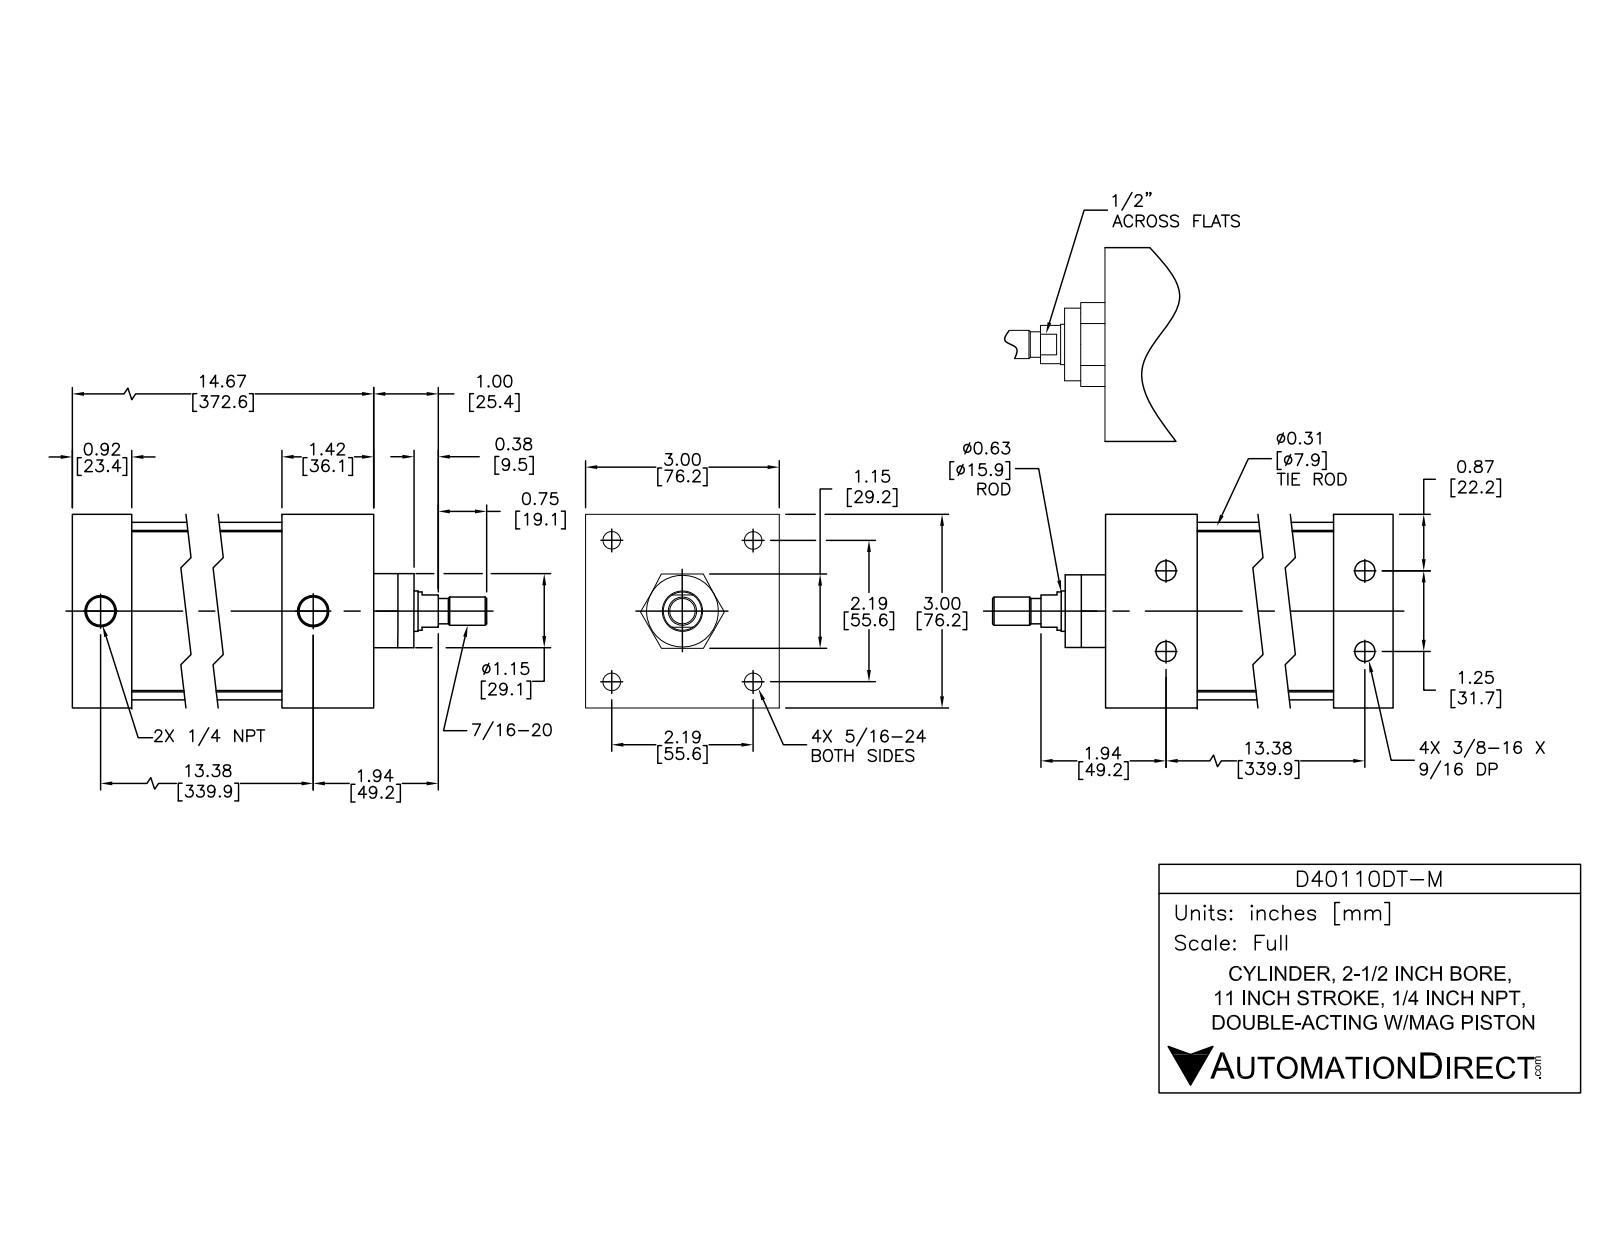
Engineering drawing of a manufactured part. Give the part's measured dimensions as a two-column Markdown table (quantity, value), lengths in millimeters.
| quantity | value |
| --- | --- |
| part name | D40110DT-M PISTON; D40110DT-M; D40110DT-M BODY |
| STEP written by | SolidWorks 2015 (AUTOMOTIVE_DESIGN) |
| units | millimeters |
| bodies | 12 solids, 298 faces (94 planar, 114 cylindrical, 90 other) |
| overall size | 419 × 76.2 × 76.2 |
| volume | 764 300 mm³ |
| surface area | 254 600 mm² |
| round holes (diameter × count) | 6.8 × 4, 7.8 × 4, 9.1 × 4, 12.7 × 4, 7.5 × 2, 12.1 × 2, 15.9 × 1, 16 × 1, 63.5 × 1 |
| round bosses / shafts (diameter × count) | 12.3 × 4, 8 × 4, 7.2 × 4, 69.9 × 1, 63.4 × 1, 28.4 × 1, 15.8 × 1, 15 × 1 |
| partial cylindrical surfaces (radius × count) | 7.6 × 4 |
| main face-to-face distances | 76.2, 2, 313.1, 374.5, 348.6, 25.9, 36.1, 312.6, 338.5, 25.4 |
| hole center spacings | 39.5, 55.9, 340, 339.6, 15.9, 15.9, 31.8, 79 |
